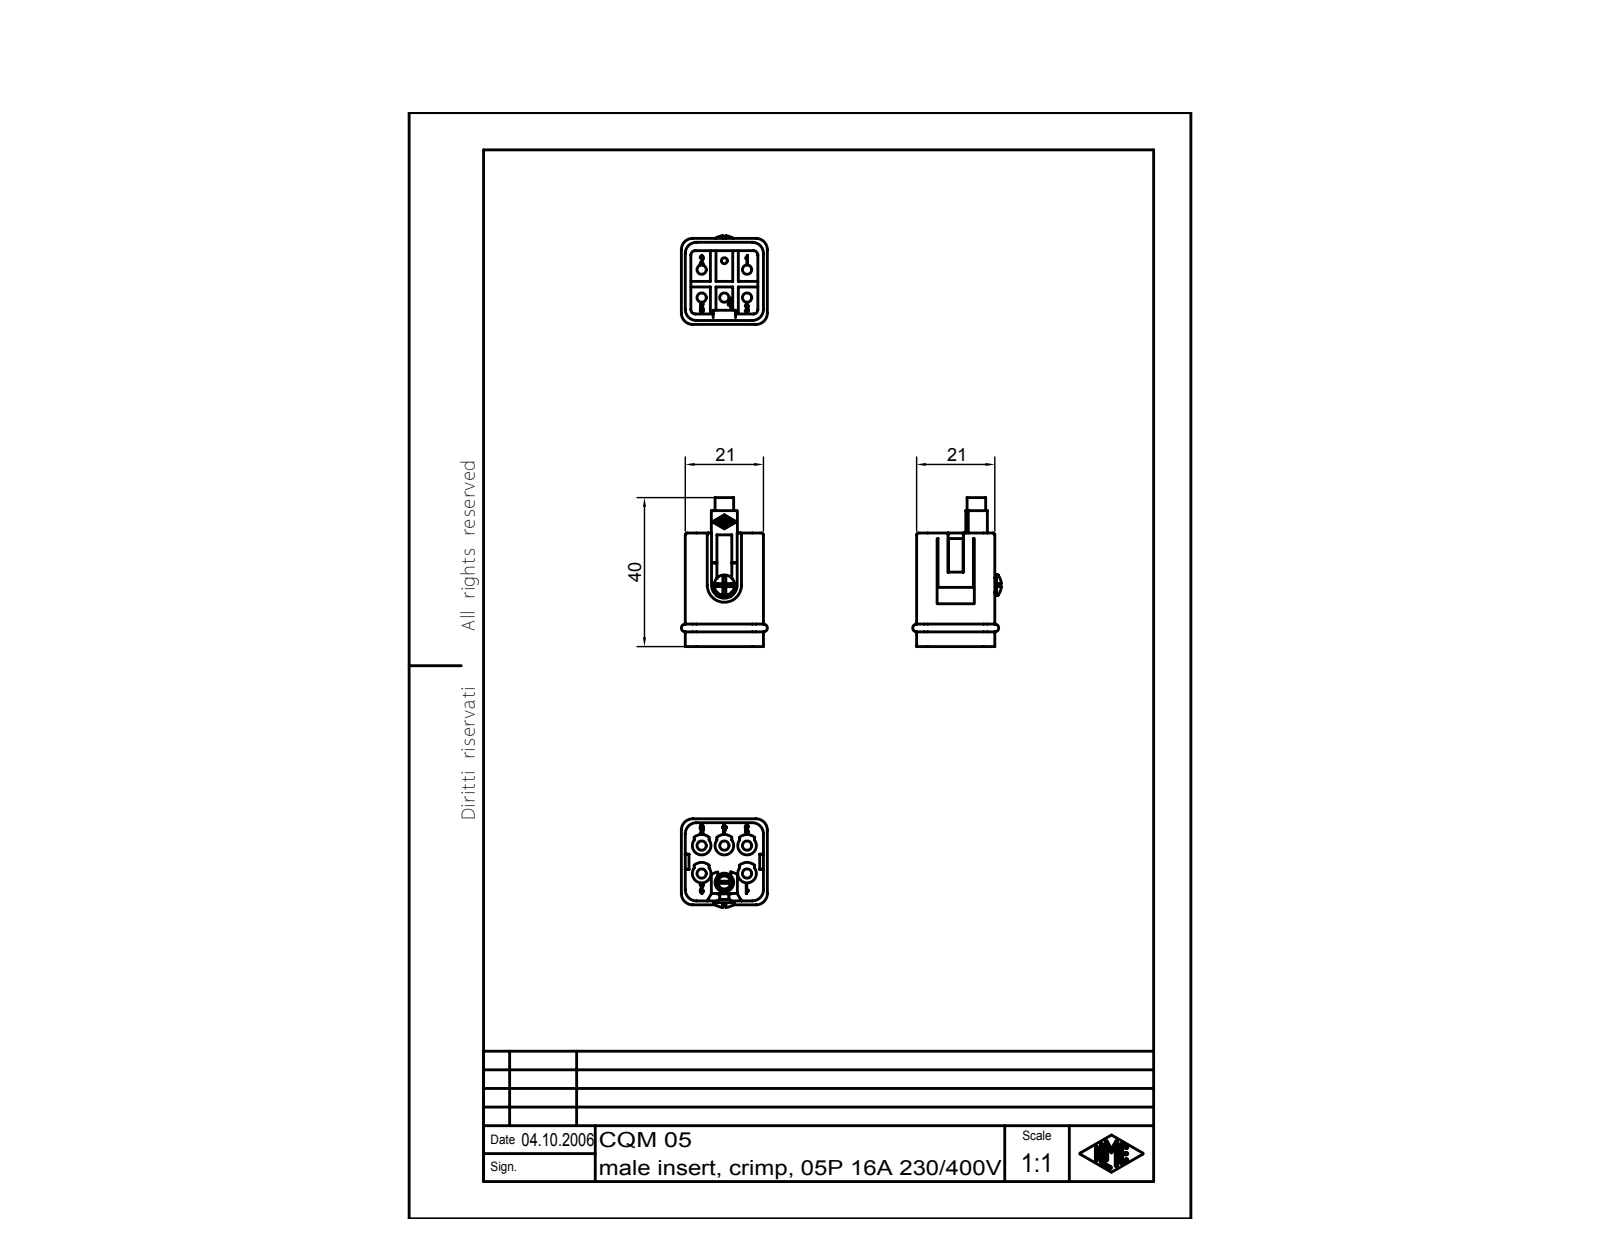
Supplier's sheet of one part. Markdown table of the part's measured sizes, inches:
| quantity | value |
| --- | --- |
| part name | CQM 05 |
| STEP written by | Autodesk Inventor 7 (AUTOMOTIVE_DESIGN) |
| units | inches |
| bodies | 1 solid, 488 faces (246 planar, 120 cylindrical, 122 other) |
| overall size | 1.575 × 0.937 × 0.909 |
| volume | 0.506 in³ |
| surface area | 10.44 in² |
| round holes (diameter × count) | 0.098 × 5, 0.118 × 1, 0.157 × 1 |
| round bosses / shafts (diameter × count) | 0.083 × 4, 0.217 × 1, 0.197 × 1, 0.138 × 1, 0.098 × 1, 0.063 × 1 |
| partial cylindrical surfaces (radius × count) | 0.005 × 14, 0.118 × 9, 0.098 × 5, 0.02 × 4, 0.039 × 4, 0.047 × 4, 0.079 × 4, 0.295 × 1 |
| main face-to-face distances | 0.827, 0.059, 0.236, 0.768, 0.079, 0.217, 0.039, 0.157, 0.807, 0.728 |
| hole center spacings | 0.24, 0.258, 0.295, 0.381, 0.458, 0.48, 0.564, 0.39 |
